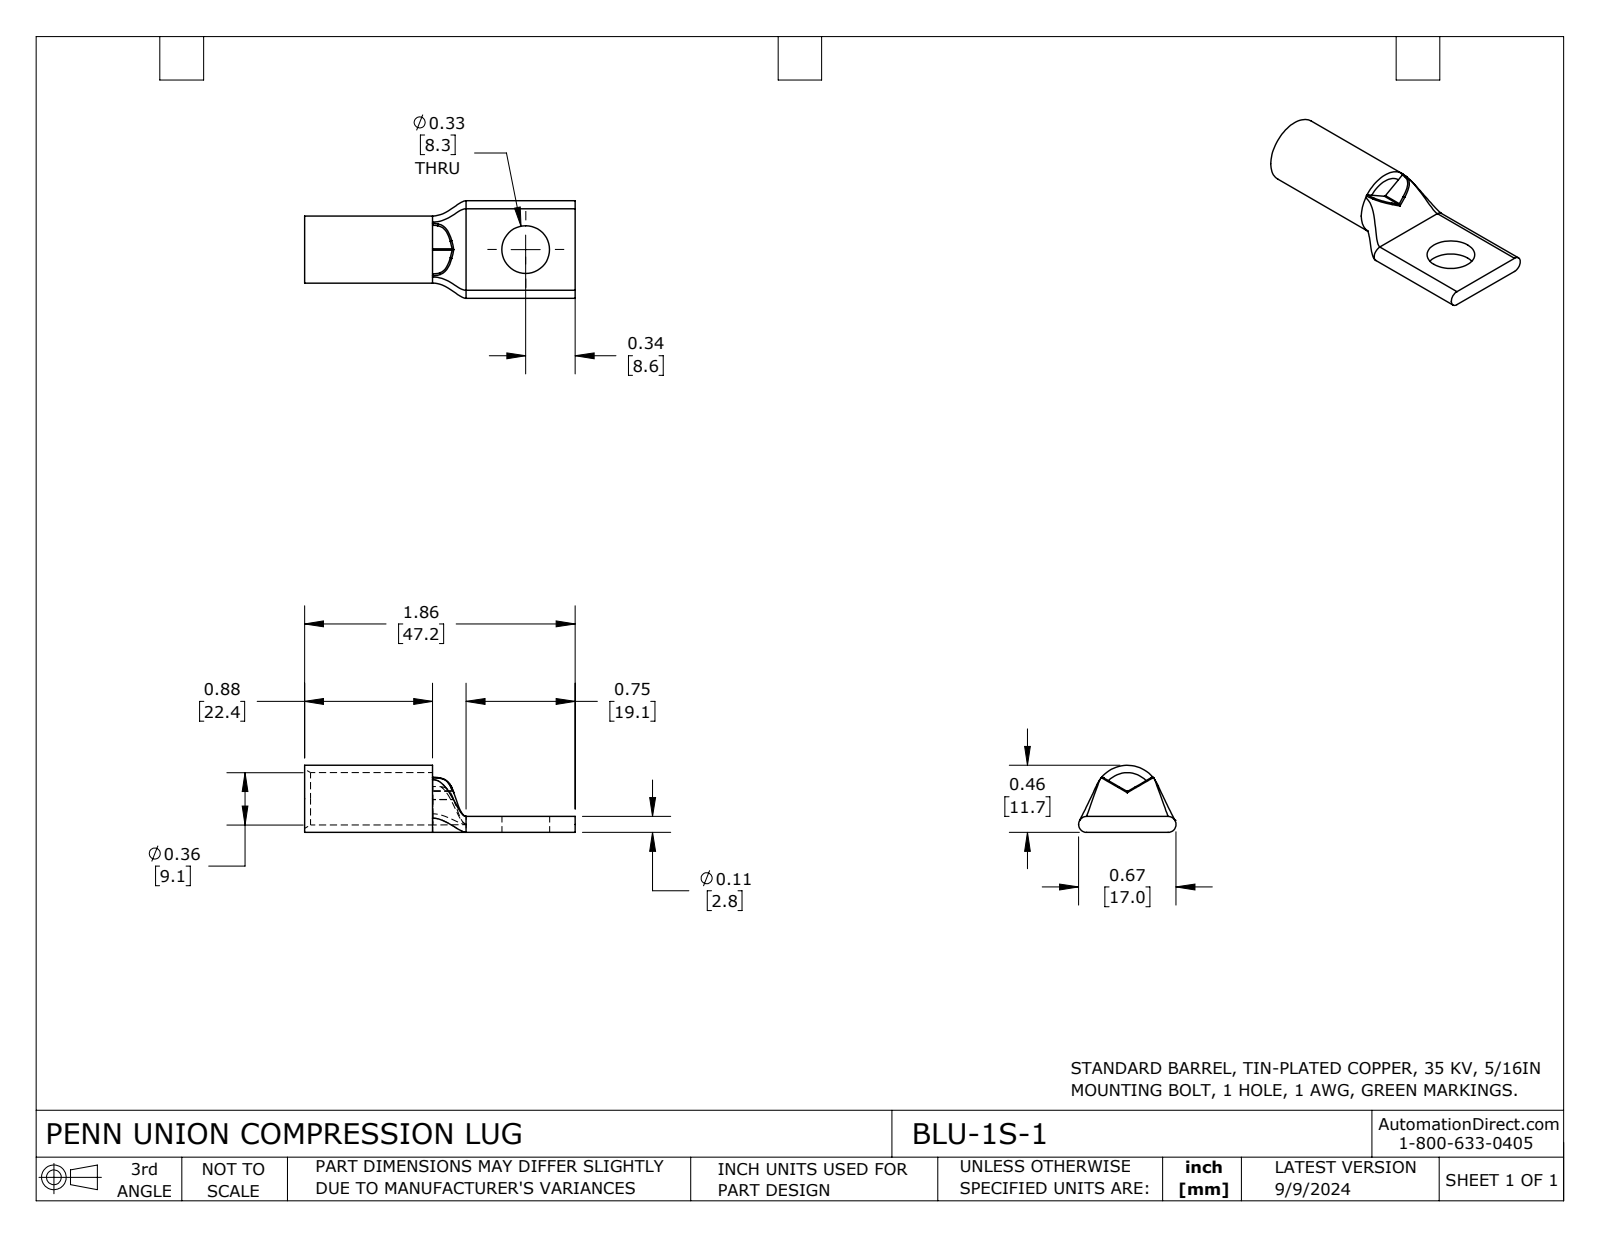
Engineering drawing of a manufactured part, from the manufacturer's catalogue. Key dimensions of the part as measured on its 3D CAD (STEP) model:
Part name (STEP PRODUCT): BLU-1S-1
STEP written by: SolidWorks 2023 (CONFIG_CONTROL_DESIGN)
Units: inches
Bodies: 1 solid, 41 faces (11 planar, 11 cylindrical, 19 other)
Overall size (bounding box): 1.86 × 0.67 × 0.461
Volume: 0.116 in³ · Surface area: 4.21 in²
Round holes (diameter × count): ⌀0.328 ×1, ⌀0.36 ×1
Round bosses / shafts (diameter × count): ⌀0.461 ×1
Partial cylindrical surfaces — rounded edges, fillets, slot ends (radius × count): R0.01 ×2, R0.055 ×2
Main face-to-face distances: 0.11, 0.05, 1.86, 0.88, 0.98, 1.11, 0.23, 0.75
